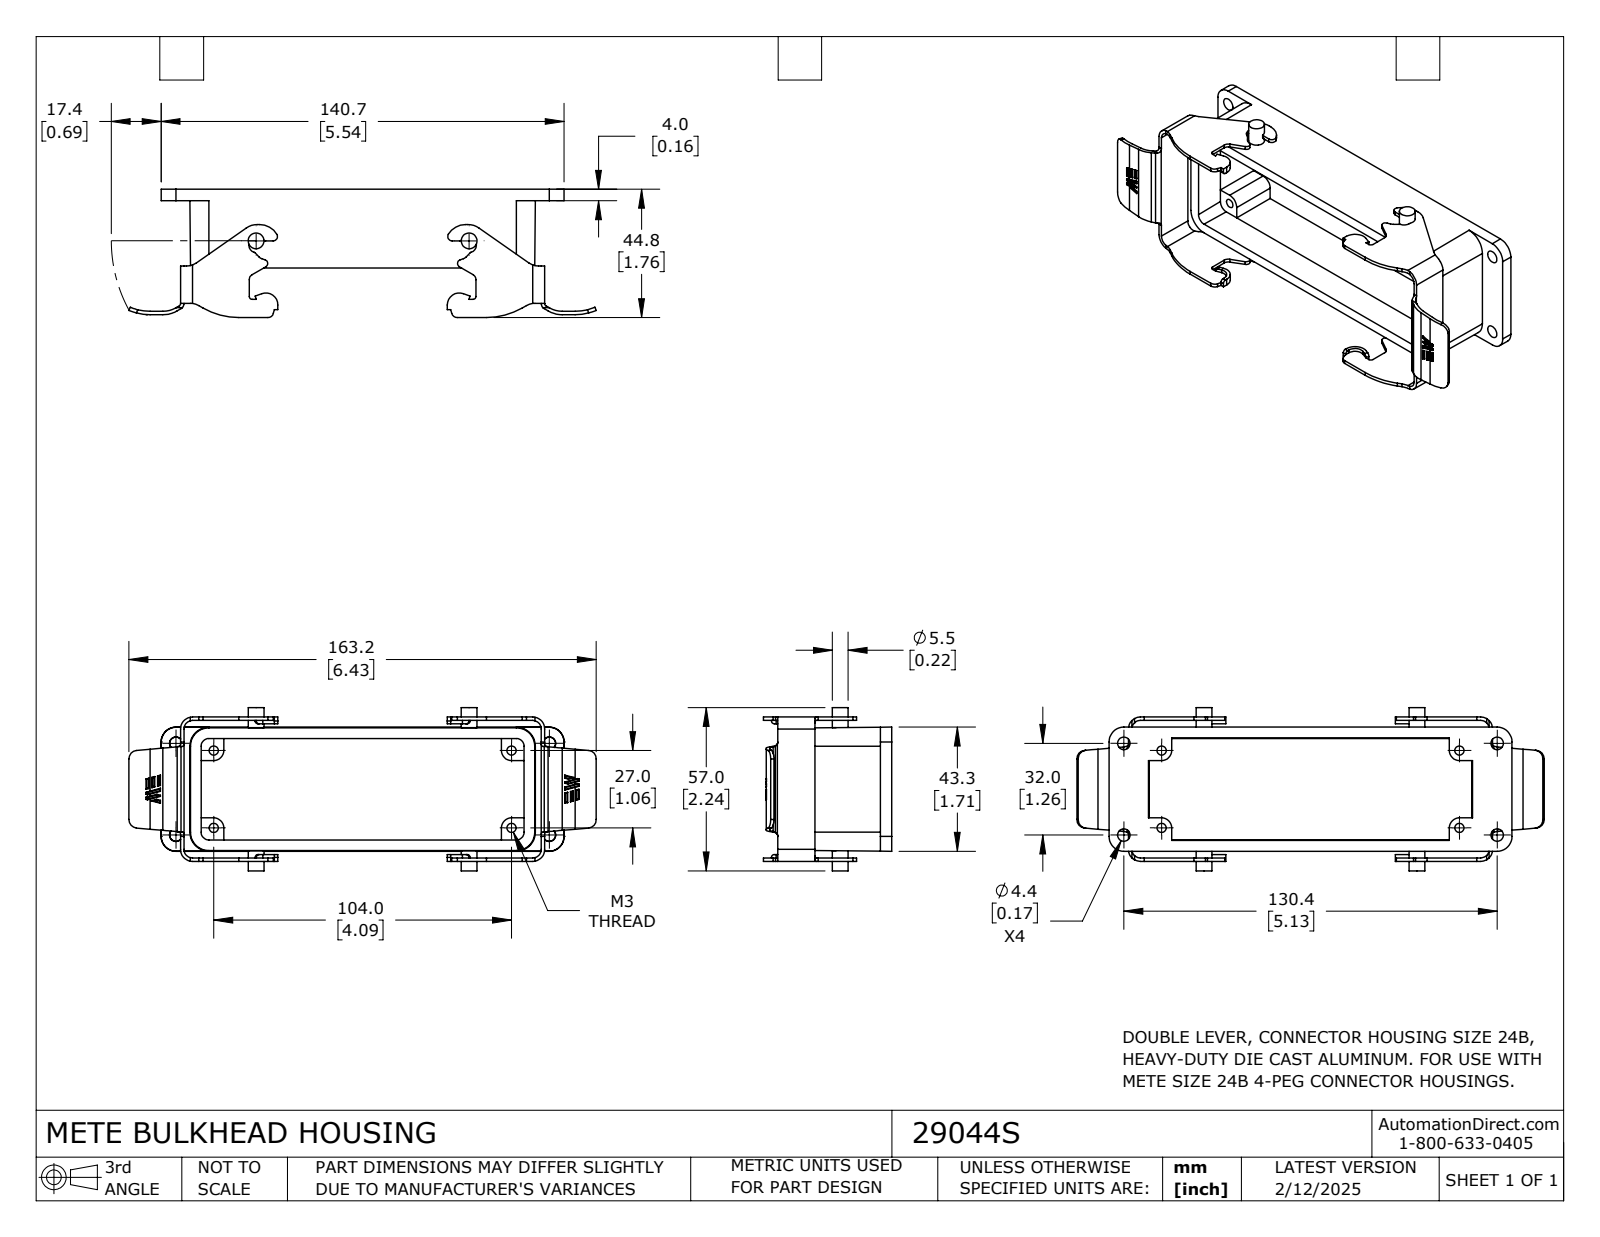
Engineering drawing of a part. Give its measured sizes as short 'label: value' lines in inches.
name: 29044S
written by: SolidWorks 2024 (CONFIG_CONTROL_DESIGN)
unit: in
bodies: 1 solid, 362 faces (162 planar, 172 cylindrical, 28 other)
size: 6.425 × 2.244 × 1.764
volume: 2.699 in³; area: 51.91 in²
holes: 4× ⌀0.126
bosses: 2× ⌀0.217
rounds: 32× R0.008, 10× R0.039, 10× R0.118, 6× R0.059, 6× R0.079, 6× R0.165, 4× R0.098, 4× R0.138
face distances: 0.047, 0.287, 1.697, 1.937, 0.24, 1.65, 1.409, 1.89, 1.984, 1.083
hole spacings: 1.063, 4.094, 4.23
